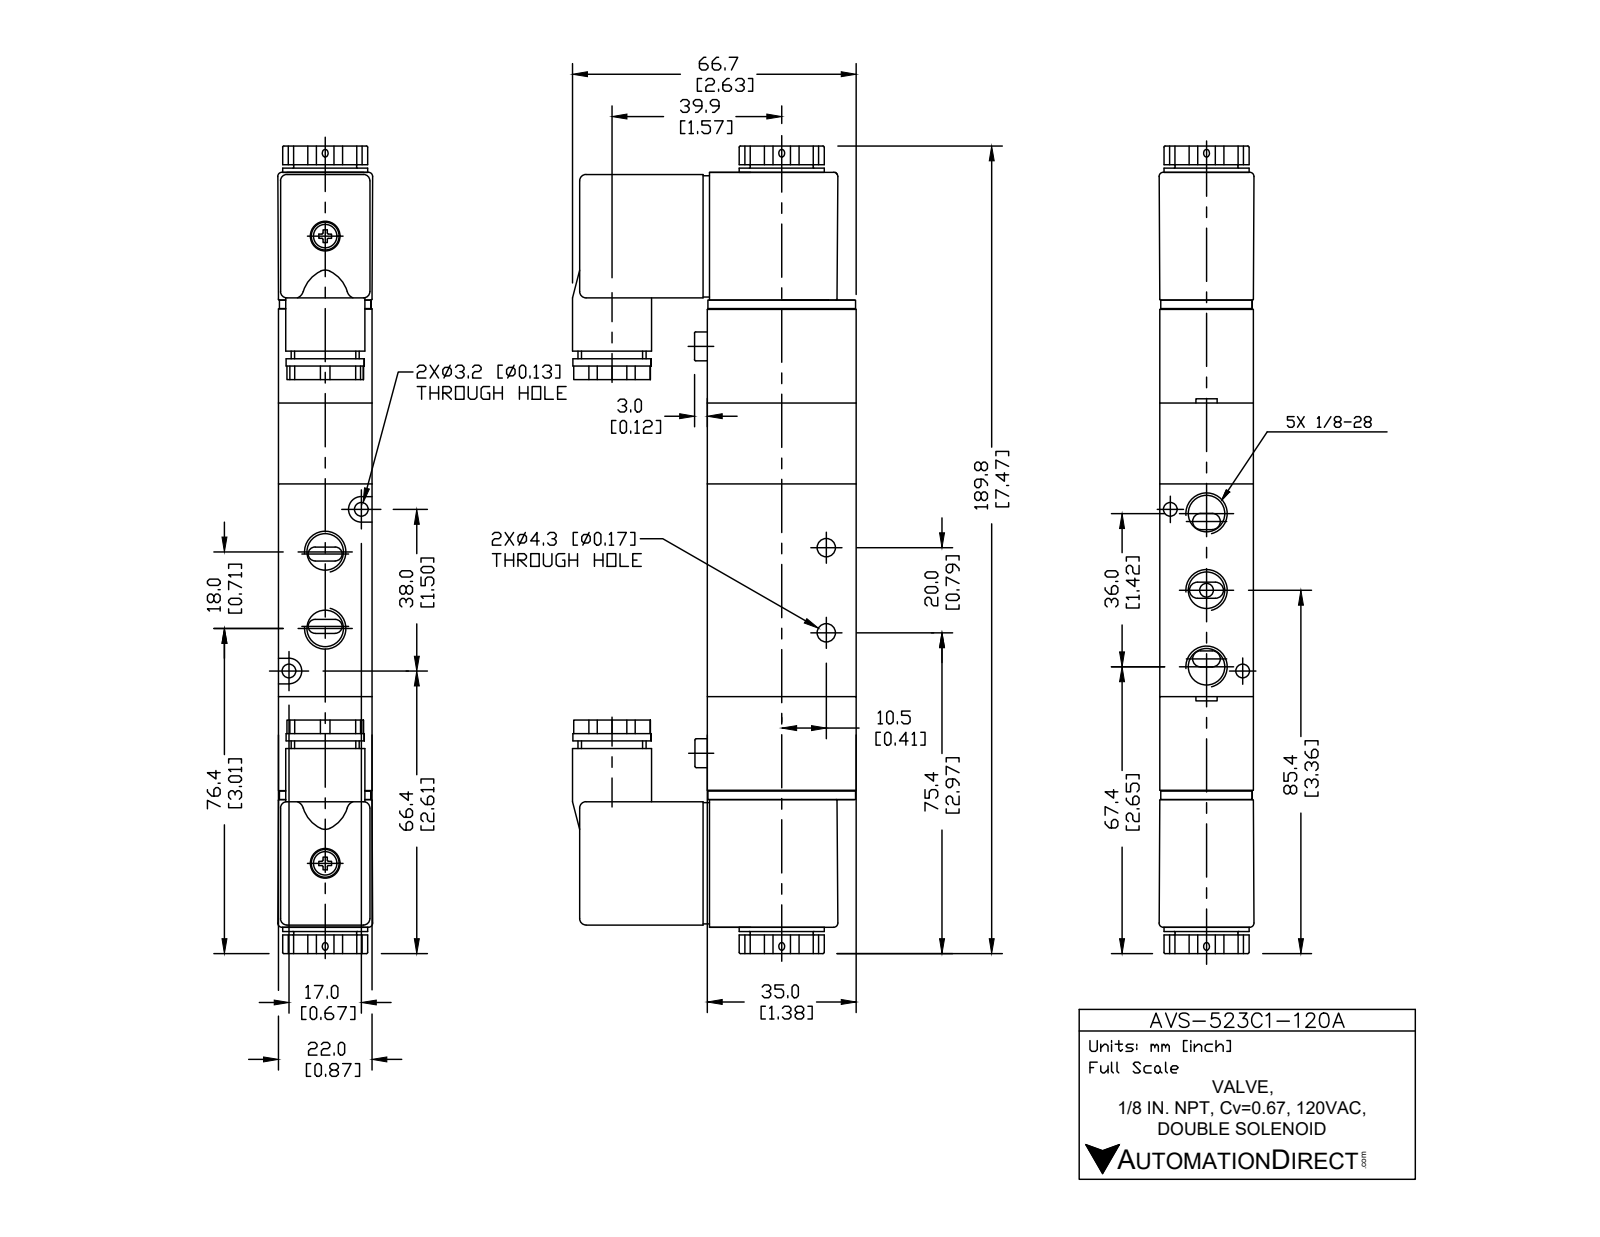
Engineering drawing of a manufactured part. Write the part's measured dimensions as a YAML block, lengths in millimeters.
part_name: "AVS-523C1-120A"
step_written_by: "SolidWorks 2015 (CONFIG_CONTROL_DESIGN)"
units: millimeters
bodies: {solids: 5, faces: 236, planar: 129, cylindrical: 91, other: 16}
overall_size: [189.82, 66.7, 22]
volume: 150497
surface_area: 37557
round_holes:
  - {diameter: 8.43, count: 5}
  - {diameter: 3.2, count: 2}
  - {diameter: 4.3, count: 2}
  - {diameter: 9.3, count: 1}
round_bosses_or_shafts:
  - {diameter: 6.8, count: 2}
  - {diameter: 18.6, count: 1}
  - {diameter: 17.6, count: 1}
  - {diameter: 15.81, count: 1}
  - {diameter: 13.02, count: 1}
  - {diameter: 11, count: 1}
partial_cylinders:
  - {radius: 1.54, count: 10}
  - {radius: 0.3, count: 8}
  - {radius: 0.5, count: 8}
  - {radius: 1, count: 8}
  - {radius: 3, count: 2}
face_to_face_distances: [0.88, 21.74, 1.95, 20.05, 22, 18.1, 22.62, 69, 30.59, 5.03]
hole_center_spacings: [8.56, 18, 20.81, 37.96, 7.54, 7.83, 10.53, 10.55]
